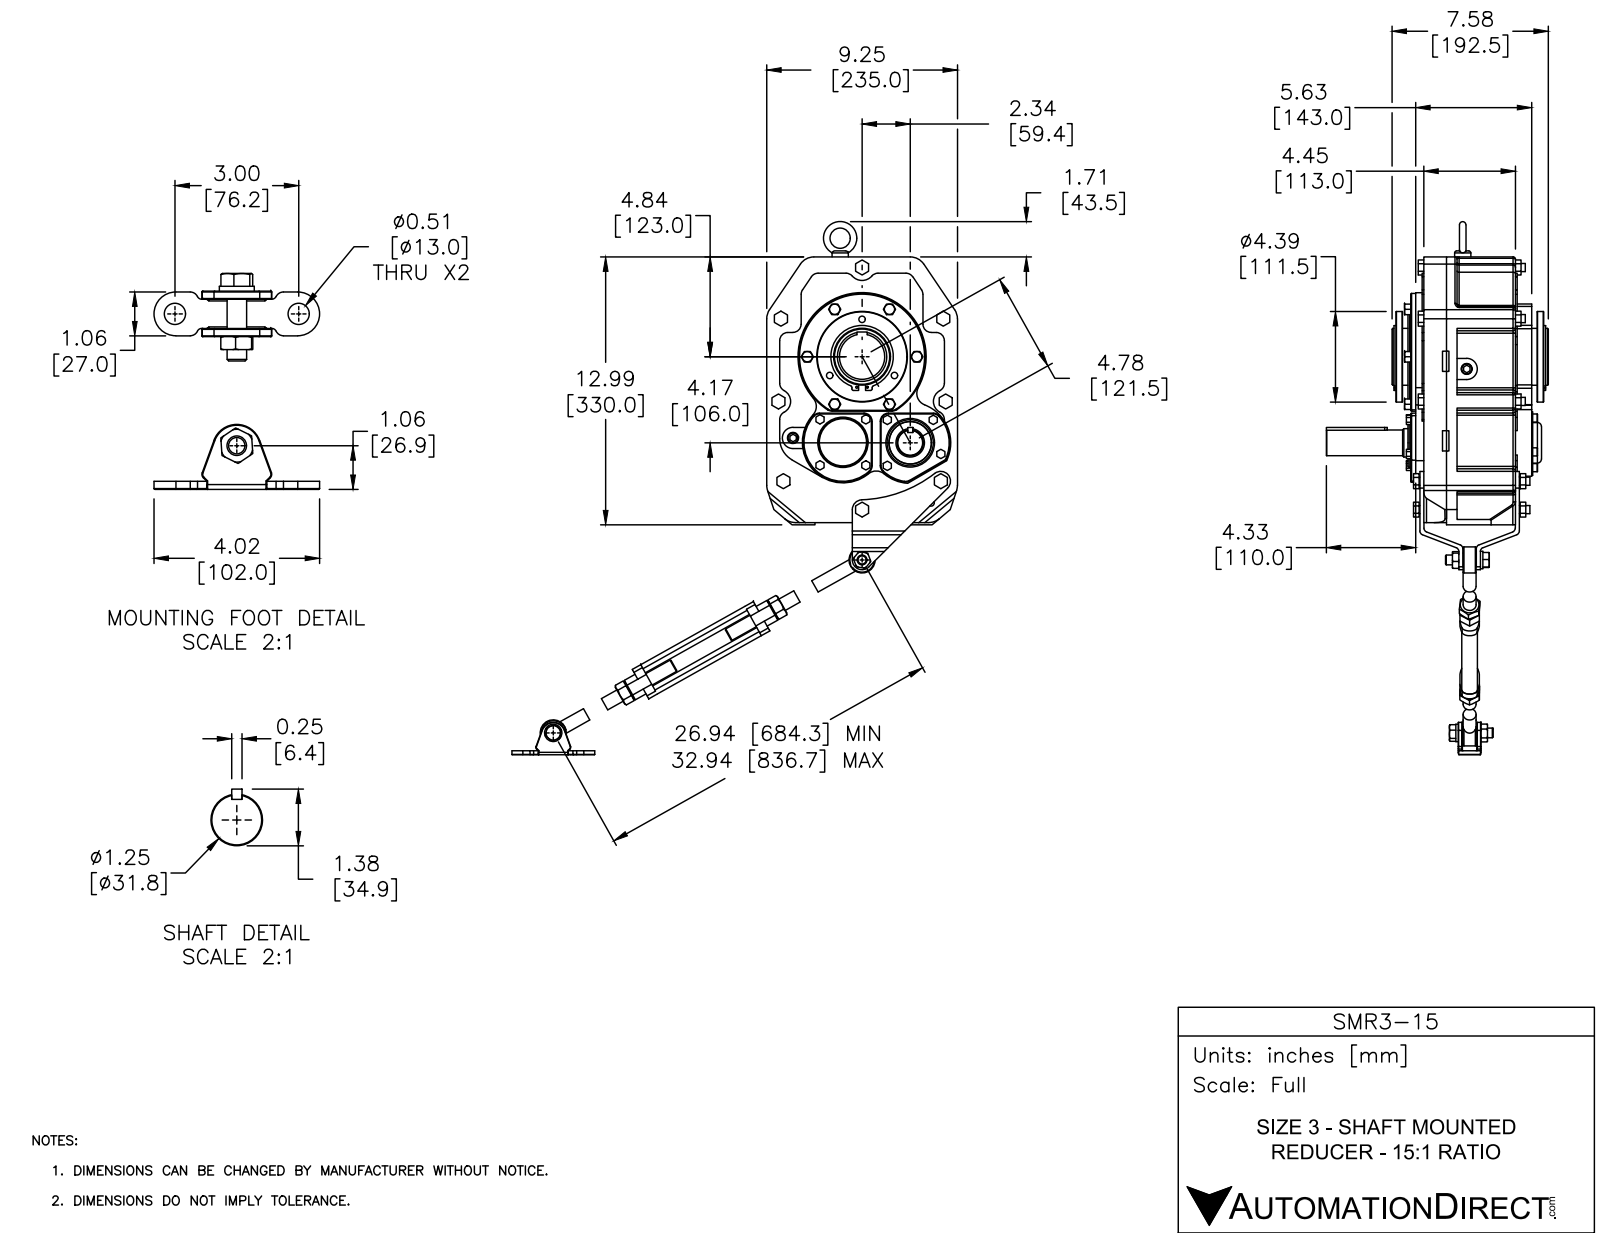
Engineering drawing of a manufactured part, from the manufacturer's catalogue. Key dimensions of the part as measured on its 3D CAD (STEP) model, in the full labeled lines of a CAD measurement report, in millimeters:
Part name (STEP PRODUCT): SMR3-15; SMR3-TA; SMR3-TA_5; SMR3-TA_4 (+4 more)
STEP written by: SolidWorks 2016 (AUTOMOTIVE_DESIGN)
Units: millimetres
Bodies: 71 solids, 1559 faces (727 planar, 556 cylindrical, 276 other)
Overall size (bounding box): 860.9 × 831.4 × 273.5
Volume: 8 860 000 mm³ · Surface area: 916 800 mm²
Round holes (diameter × count): ⌀10 ×8, ⌀11 ×8, ⌀8 ×7, ⌀13 ×5, ⌀12.7 ×4, ⌀2.5 ×2, ⌀12 ×2, ⌀12.2 ×2, ⌀12.9 ×2, ⌀13.3 ×2, ⌀16 ×2, ⌀8 ×1
Round bosses / shafts (diameter × count): ⌀13 ×5, ⌀10 ×4, ⌀60 ×2, ⌀50 ×2, ⌀32 ×2, ⌀22.3 ×2, ⌀21.5 ×2, ⌀16 ×2
Partial cylindrical surfaces — rounded edges, fillets, slot ends (radius × count): R3 ×80, R10 ×35, R0.5 ×22, R5 ×16, R2.5 ×12, R20 ×10, R15 ×9, R1 ×7
Main face-to-face distances: 10, 38, 115, 2, 28, 143, 133, 105, 8, 18
Hole centre spacings: 70, 99, 46.1, 79.7, 28.2, 36.4, 38, 44.6
